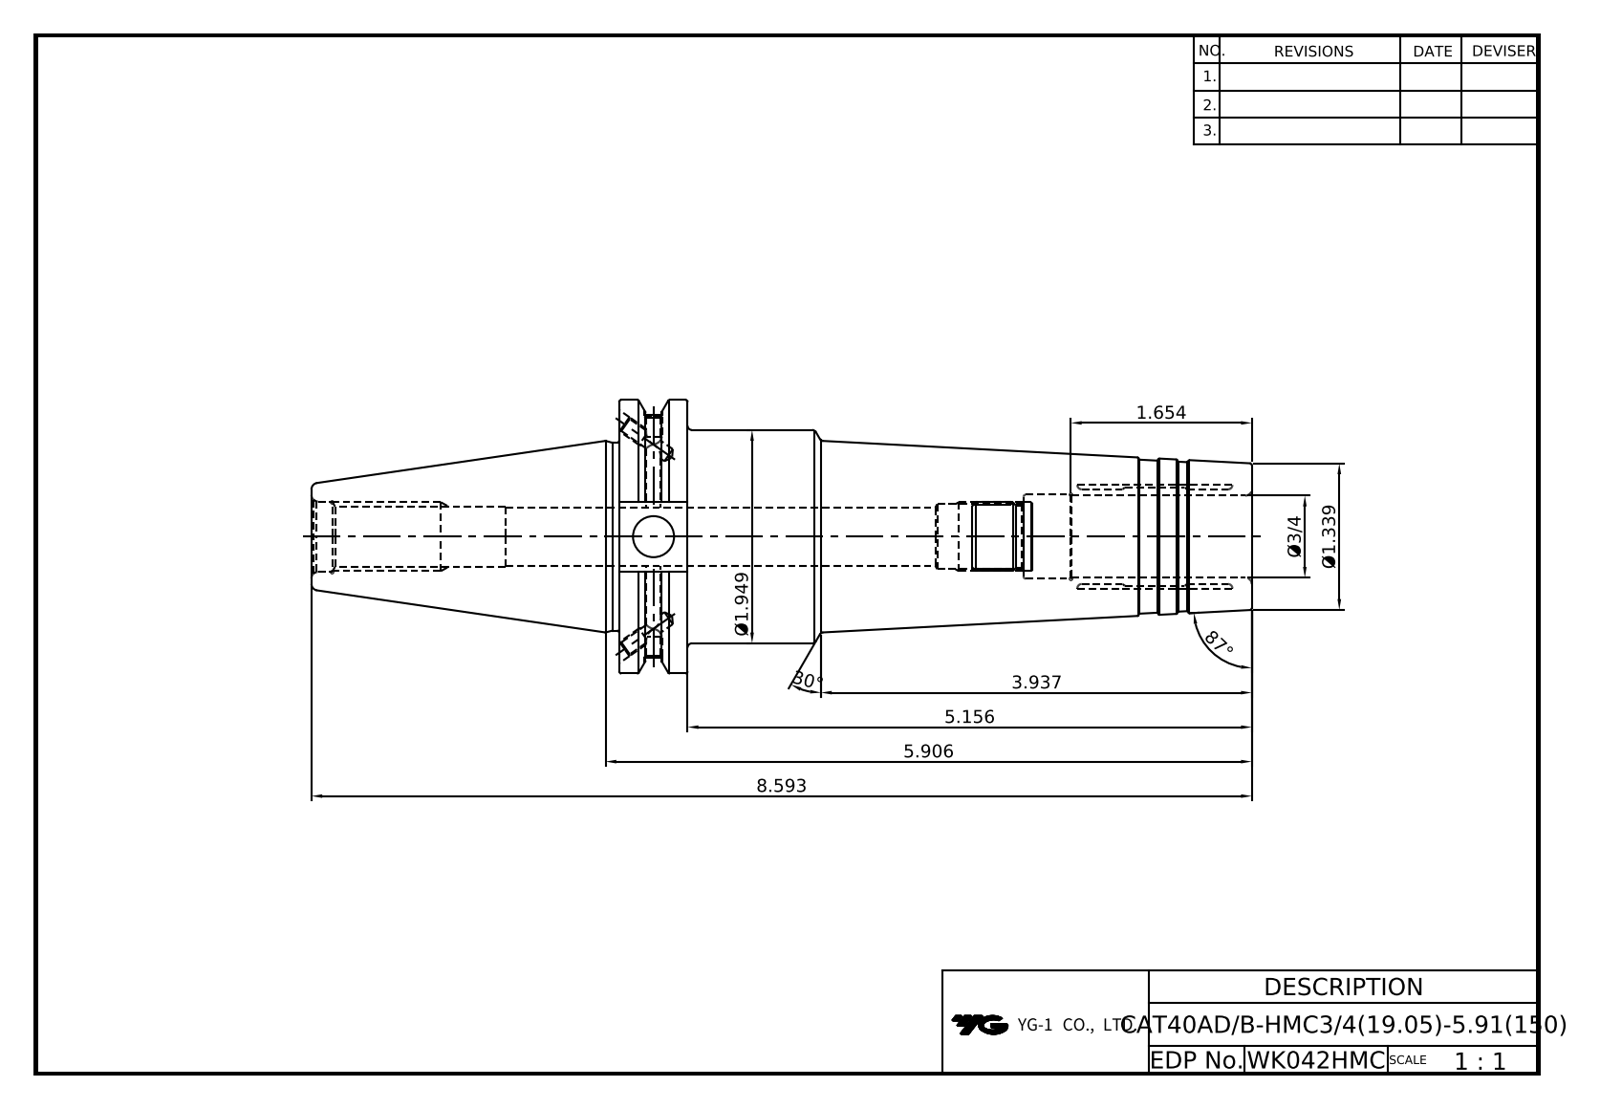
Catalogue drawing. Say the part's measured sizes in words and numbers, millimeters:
The part is named "LO-CAT40ADB-HMC19.05-150". Its 3-D file was written by "Autodesk Inventor 2020 (AUTOMOTIVE_DESIGN)". It is 1 solid with 106 faces: 36 planar, 30 cylindrical and 40 other. Overall it measures 218.25 by 63.5 by 61.09 millimeters. Its volume is 254 792 cubic millimeters and its surface area 43 514 square millimeters. Round holes: 4 of diameter 3.24, 2 of diameter 4, 2 of diameter 4.2, 1 of diameter 9.53, 1 of diameter 13, 1 of diameter 13.39, 1 of diameter 14.92, 1 of diameter 16.3, 1 of diameter 19.05, 1 of diameter 19.4. Round bosses or shafts: 1 of diameter 63.5, 1 of diameter 49.5, 1 of diameter 43.6. Partial cylindrical surfaces (rounded edges, fillets, slot ends): 1 of radius 8.19, 1 of radius 28.15. The main face-to-face distances are 15.88, 146.83, 130.95, 47.6, 16.38, 71.42, 87.3, 218.25, 165.25, 93.83.
